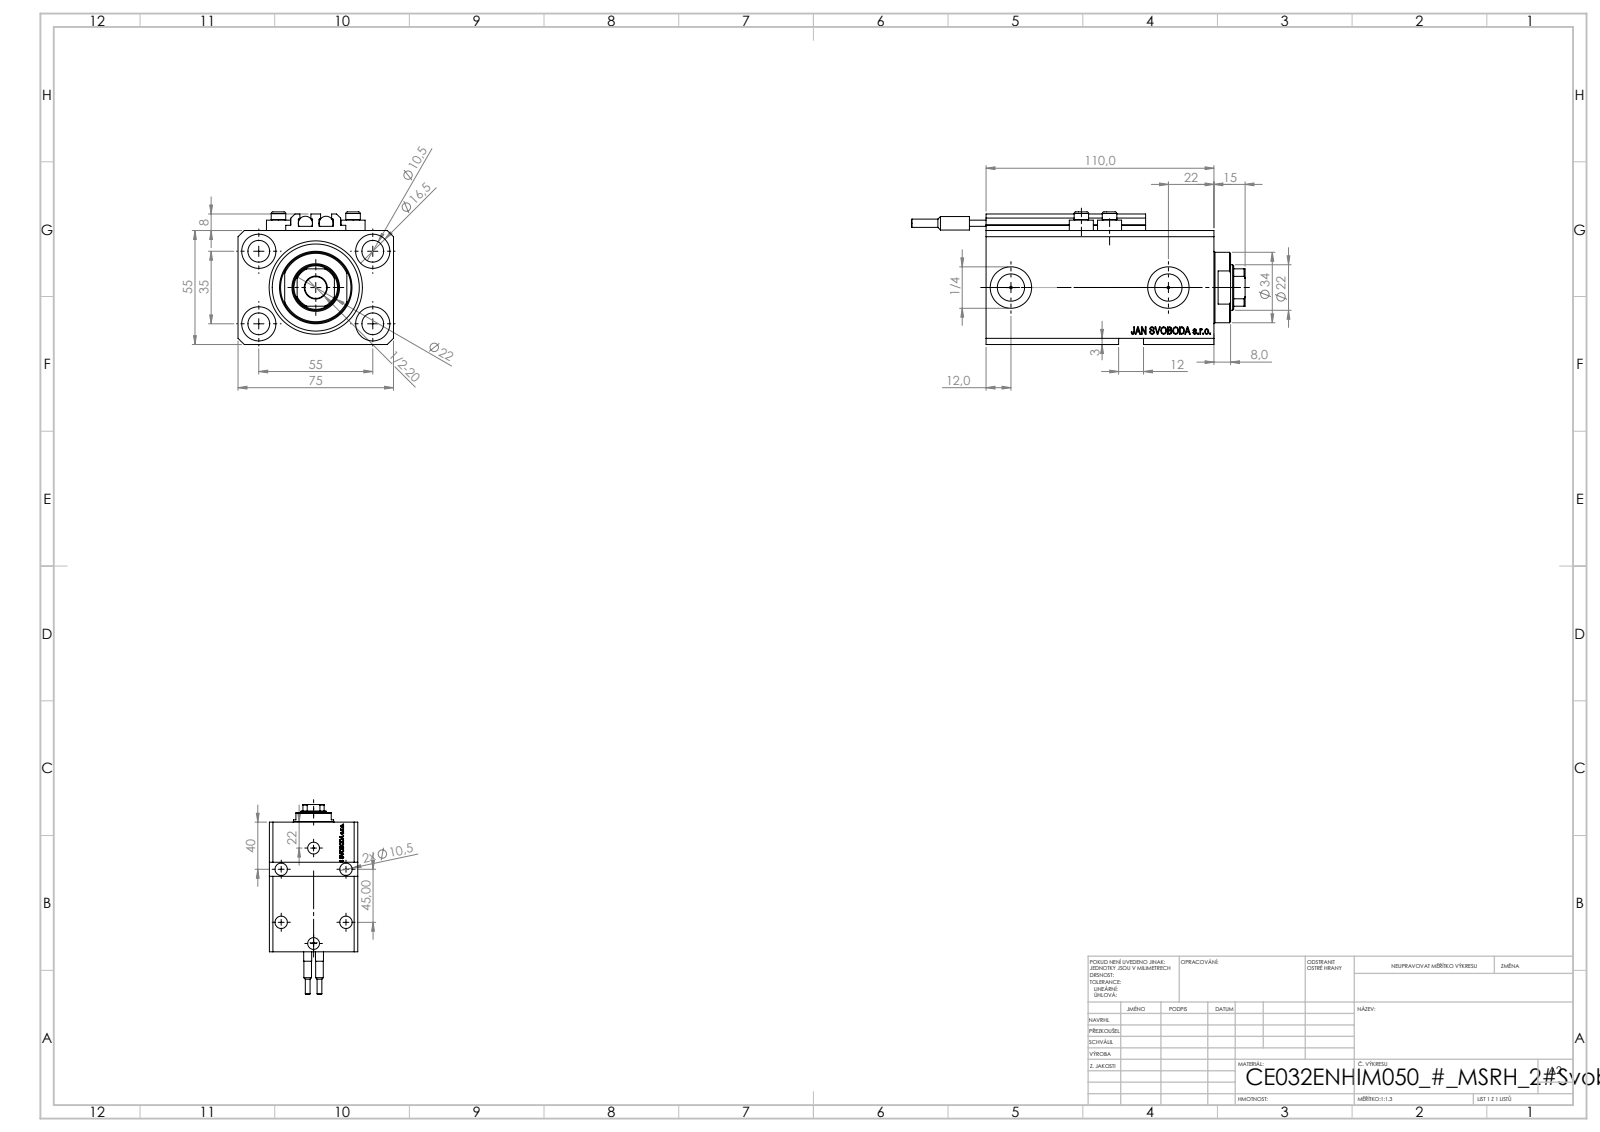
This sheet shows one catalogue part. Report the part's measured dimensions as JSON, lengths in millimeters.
{"part_name": "ALLEN BOLT V250CE; V250CE_VC_E; V250CE_E_Body; V250CE_C_VCP (+1 more)", "step_written_by": "SolidWorks 2019 (CONFIG_CONTROL_DESIGN)", "units": "millimeters", "bodies": {"solids": 10, "faces": 1136, "planar": 546, "cylindrical": 158, "other": 432}, "overall_size": [161, 75, 64], "volume_mm3": 384911, "surface_area_mm2": 98392, "round_holes": [[10.5, 9], [1.25, 4], [4, 4], [16.5, 4], [10, 2], [13.16, 2], [20, 2], [22, 1], [32, 1], [45, 1]], "round_bosses_or_shafts": [[11.6, 4], [7, 4], [6.8, 2], [6.5, 2], [4, 2], [34, 1]], "partial_cylinders_radius": [[0.2, 10], [10.5, 1]], "face_to_face_distances": [55, 75, 3, 15, 110, 57, 95, 9.9, 85.1, 100.1], "hole_center_spacings": [32.6, 32.87, 55, 68.74, 13.6, 14.09, 23.05, 25.81]}
